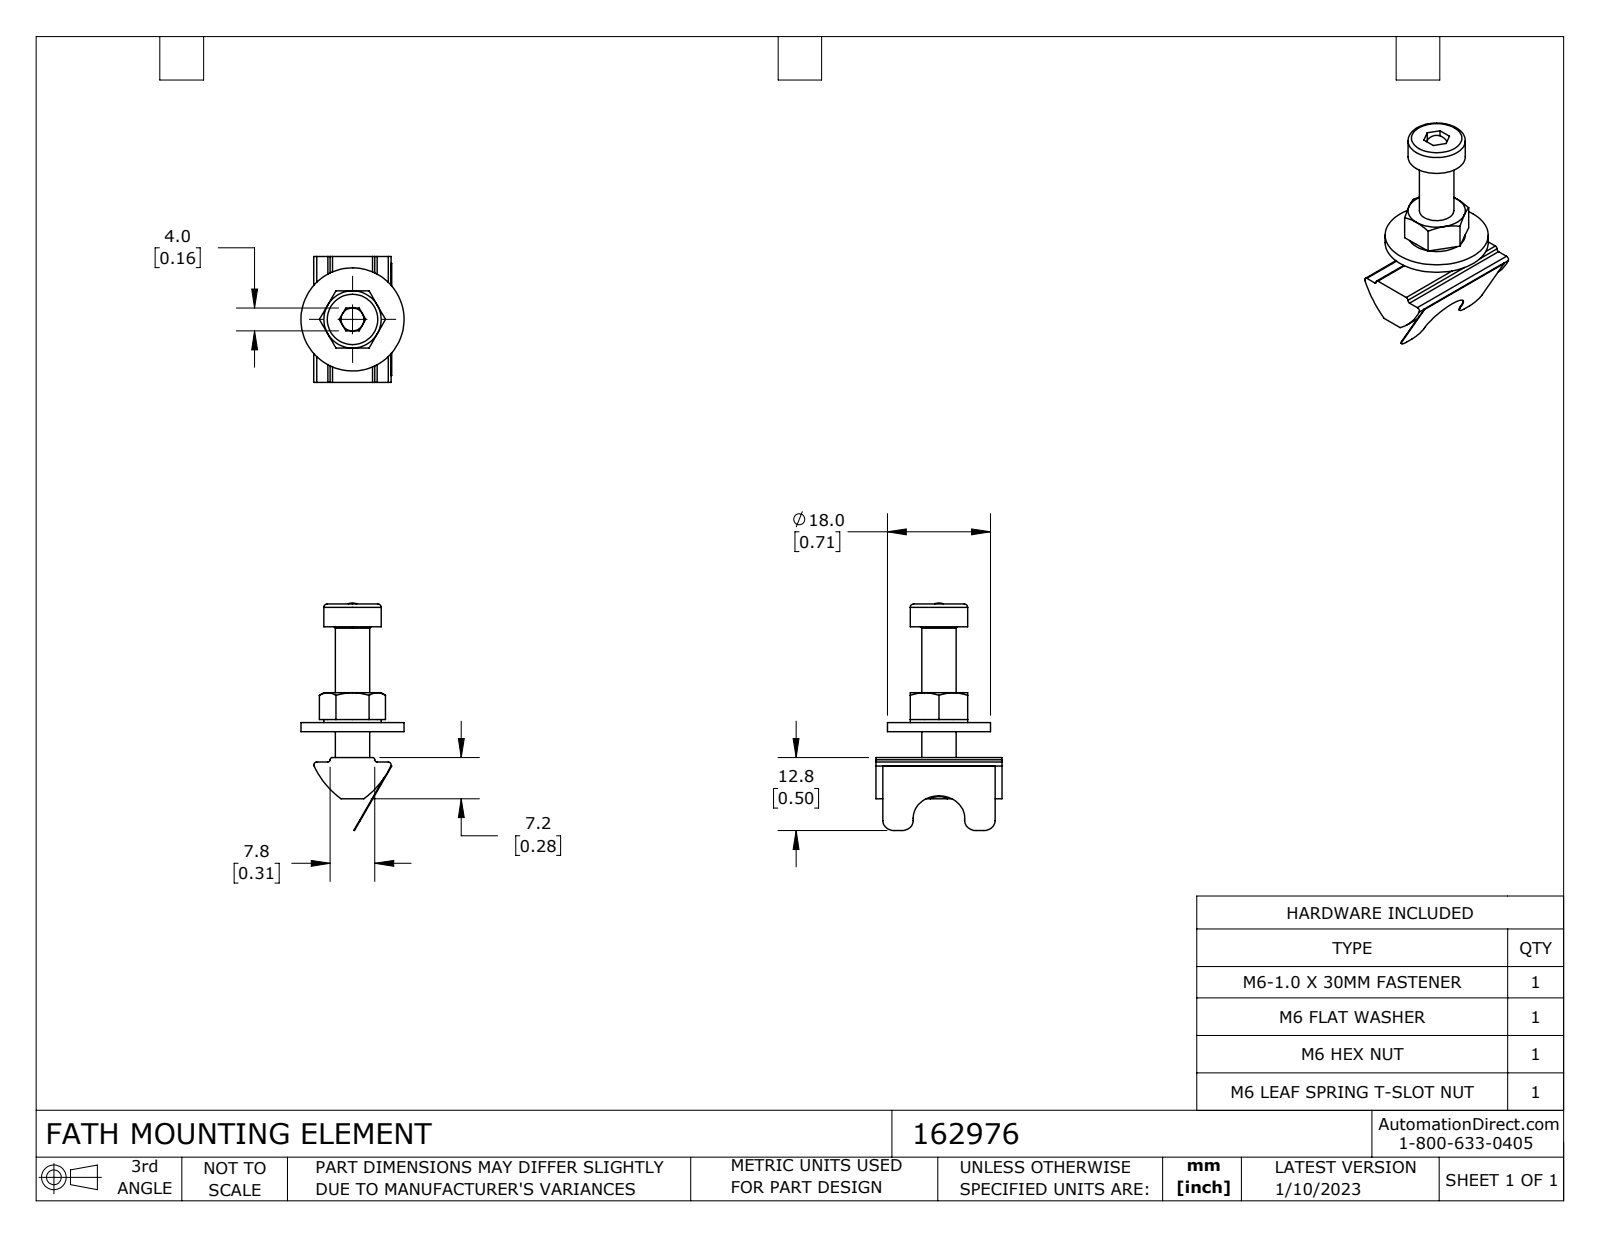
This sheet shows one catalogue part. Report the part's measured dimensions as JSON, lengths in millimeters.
{"part_name": "162976", "step_written_by": "SolidWorks 2021 (CONFIG_CONTROL_DESIGN)", "units": "millimeters", "bodies": {"solids": 5, "faces": 99, "planar": 48, "cylindrical": 30, "other": 21}, "overall_size": [39.71, 22, 18], "volume_mm3": 3248, "surface_area_mm2": 3152, "round_holes": [[5, 1], [6, 1], [6.4, 1]], "round_bosses_or_shafts": [[18, 1], [10, 1]], "partial_cylinders_radius": [[0.4, 4], [2, 4], [0.5, 2], [15, 2], [4.5, 1]], "face_to_face_distances": [1.6, 4.5, 6.1, 5.3, 0.8, 6.9, 6.4, 7.2, 11.7, 13.3]}
